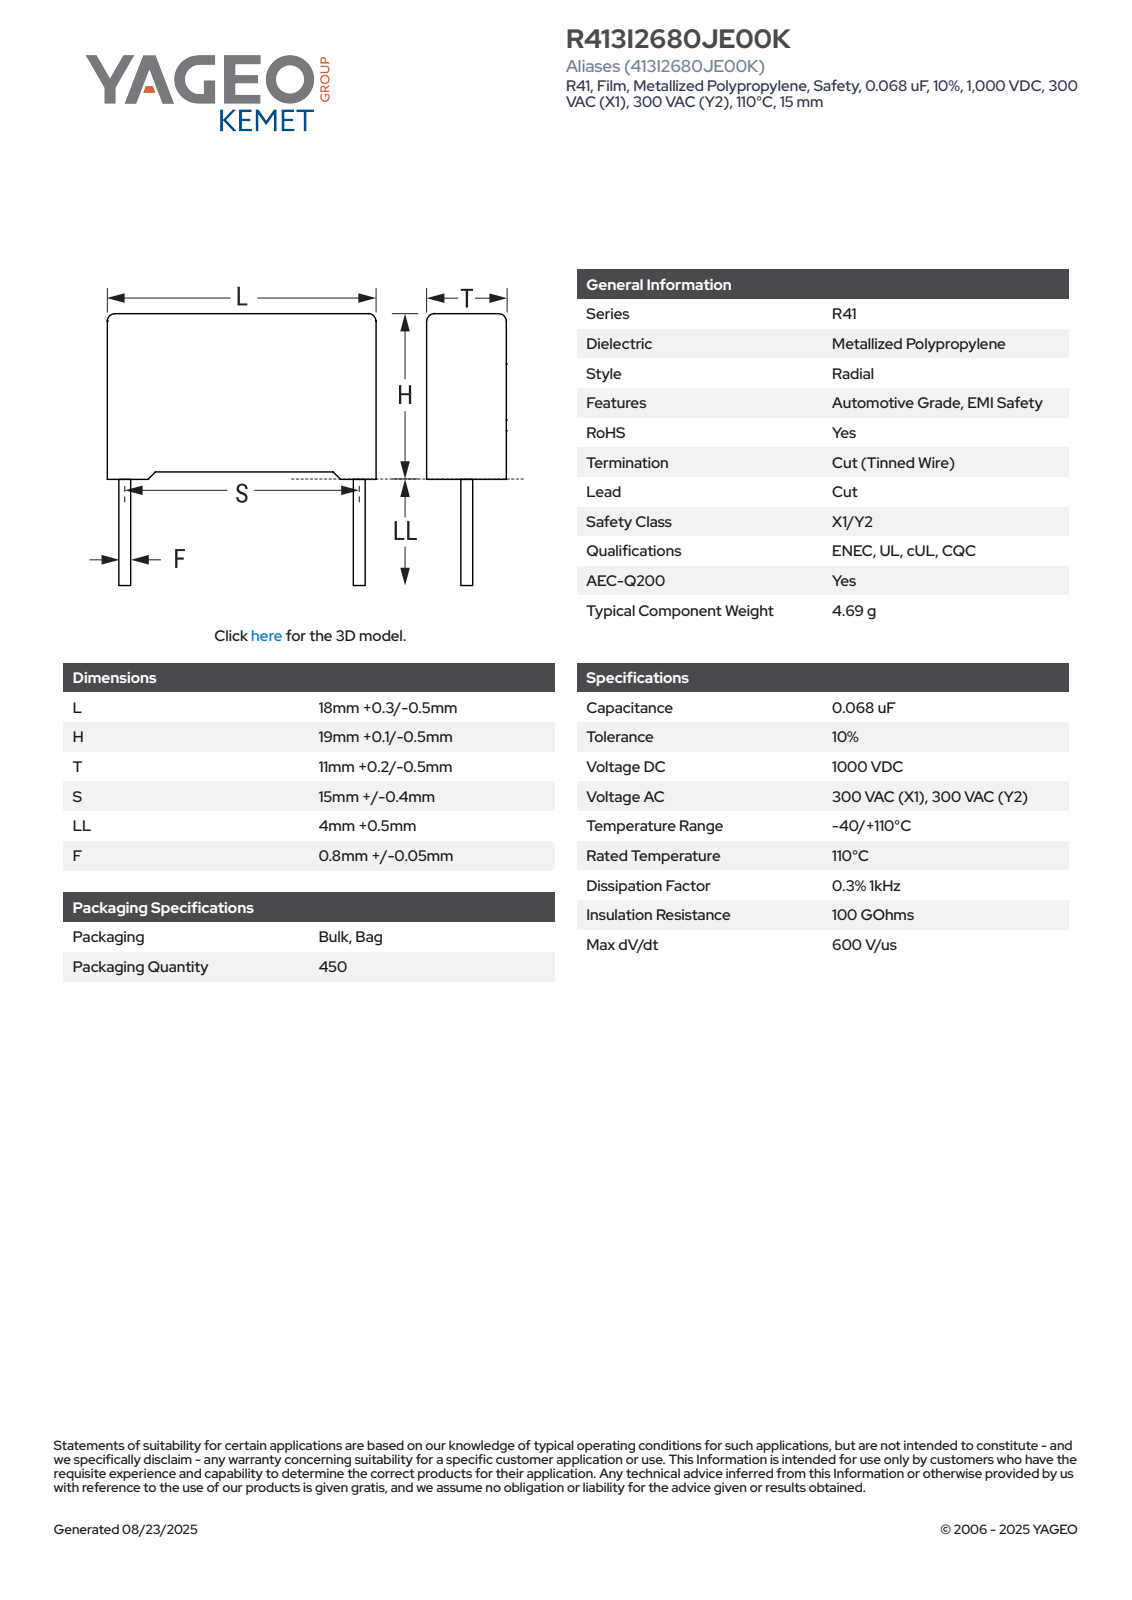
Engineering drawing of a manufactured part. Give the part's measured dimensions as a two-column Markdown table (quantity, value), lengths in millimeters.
| quantity | value |
| --- | --- |
| part name | CFR_RB2_18X19X11_L18.3H19.1T11.2S15LL4.5F0.85 |
| STEP written by | SolidWorks 2021 (AUTOMOTIVE_DESIGN) |
| units | millimeters |
| bodies | 4 solids, 85 faces (77 planar, 8 cylindrical, 0 other) |
| overall size | 23.6 × 18.3 × 11.21 |
| volume | 3 781 mm³ |
| surface area | 1 588 mm² |
| round bosses / shafts (diameter × count) | 0.85 × 2 |
| partial cylindrical surfaces (radius × count) | 0.5 × 4 |
| main face-to-face distances | 11.2, 18.3, 18.35, 0.61, 0.75, 19.1, 17.69, 0.66, 18.44, 10.59 |
